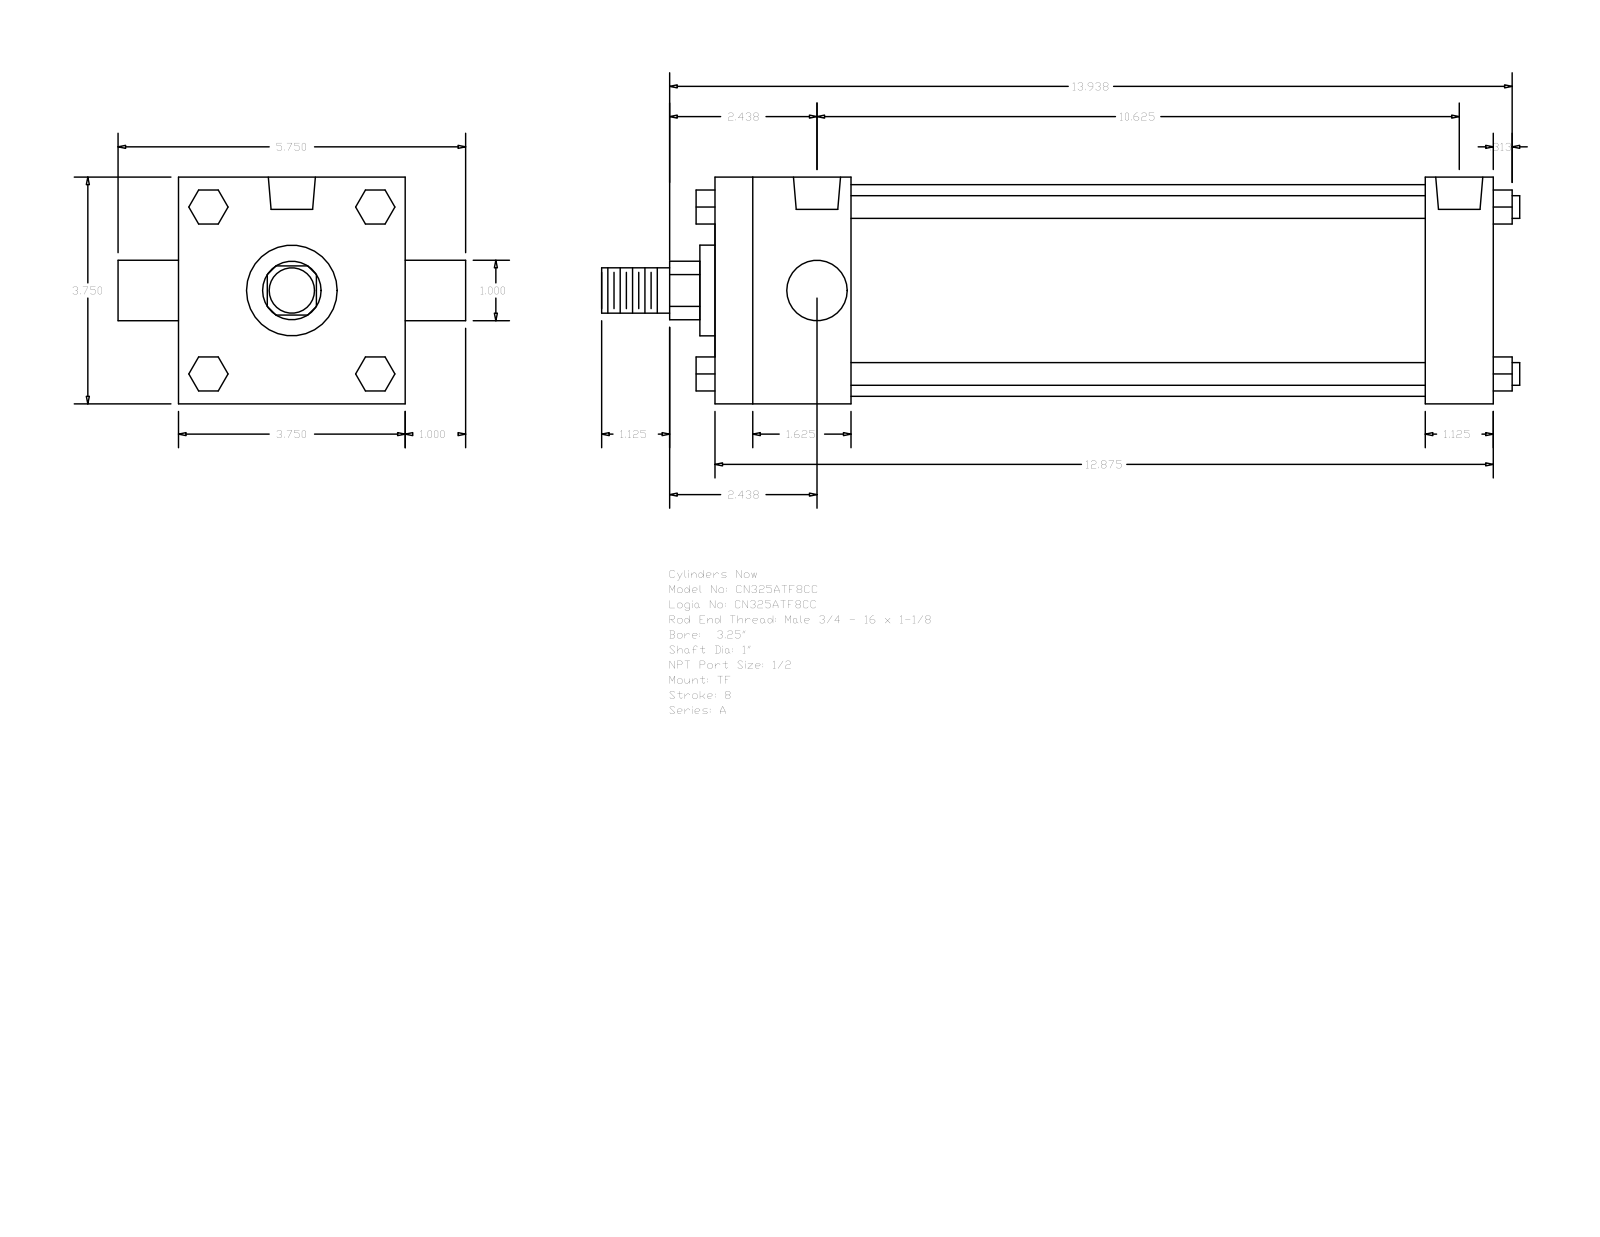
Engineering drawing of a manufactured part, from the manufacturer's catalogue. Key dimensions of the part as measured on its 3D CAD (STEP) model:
Part name (STEP PRODUCT): A_TF__0325_1
STEP written by: GSSL Pune (CONFIG_CONTROL_DESIGN)
Units: millimetres
Bodies: 0 solids, 120 faces (92 planar, 28 cylindrical, 0 other)
Overall size (bounding box): 385.76 × 146.05 × 95.25
Round holes (diameter × count): ⌀8.73 ×3, ⌀19.77 ×2
Round bosses / shafts (diameter × count): ⌀9.53 ×4, ⌀25.4 ×2, ⌀88.9 ×1, ⌀38.1 ×1, ⌀19.05 ×1
Partial cylindrical surfaces — rounded edges, fillets, slot ends (radius × count): R12.29 ×1
Main face-to-face distances: 95.24, 327.02, 28.57, 57.15, 298.45, 241.3, 269.87, 14.28, 35.05, 60.71
Hole centre spacings: 3.18, 266.7, 263.52, 269.88
